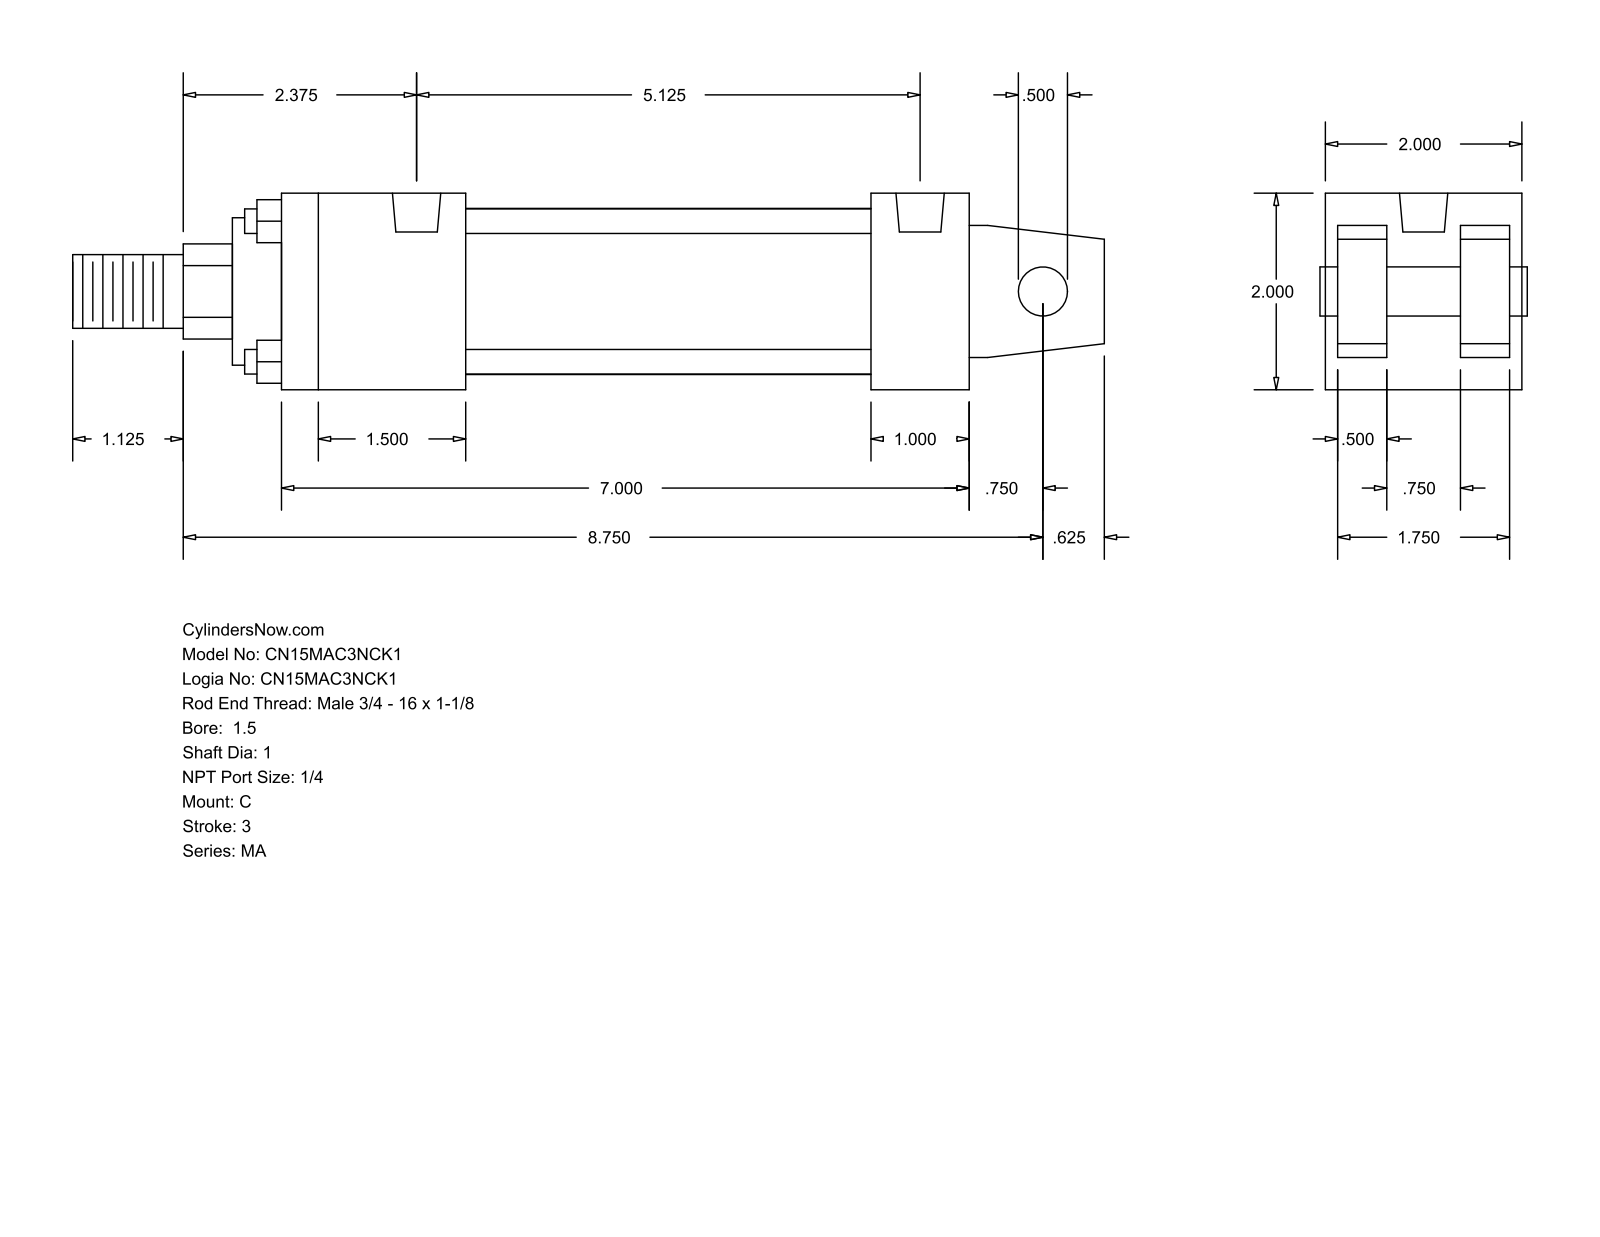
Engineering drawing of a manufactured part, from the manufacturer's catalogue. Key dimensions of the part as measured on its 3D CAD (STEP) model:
Part name (STEP PRODUCT): MA_C__0150_1
STEP written by: GSSL Pune (CONFIG_CONTROL_DESIGN)
Units: millimetres
Bodies: 0 solids, 103 faces (76 planar, 27 cylindrical, 0 other)
Overall size (bounding box): 266.7 × 50.8 × 50.8
Round holes (diameter × count): ⌀7.94 ×4, ⌀12.49 ×2
Round bosses / shafts (diameter × count): ⌀6.35 ×4, ⌀42.93 ×1, ⌀38.1 ×1, ⌀25.4 ×1, ⌀19.05 ×1, ⌀12.7 ×1
Partial cylindrical surfaces — rounded edges, fillets, slot ends (radius × count): R12.29 ×1
Main face-to-face distances: 50.8, 47.63, 12.7, 3.17, 15.87, 34.93, 31.76, 177.8, 25.4, 152.4
Hole centre spacings: 130.17
